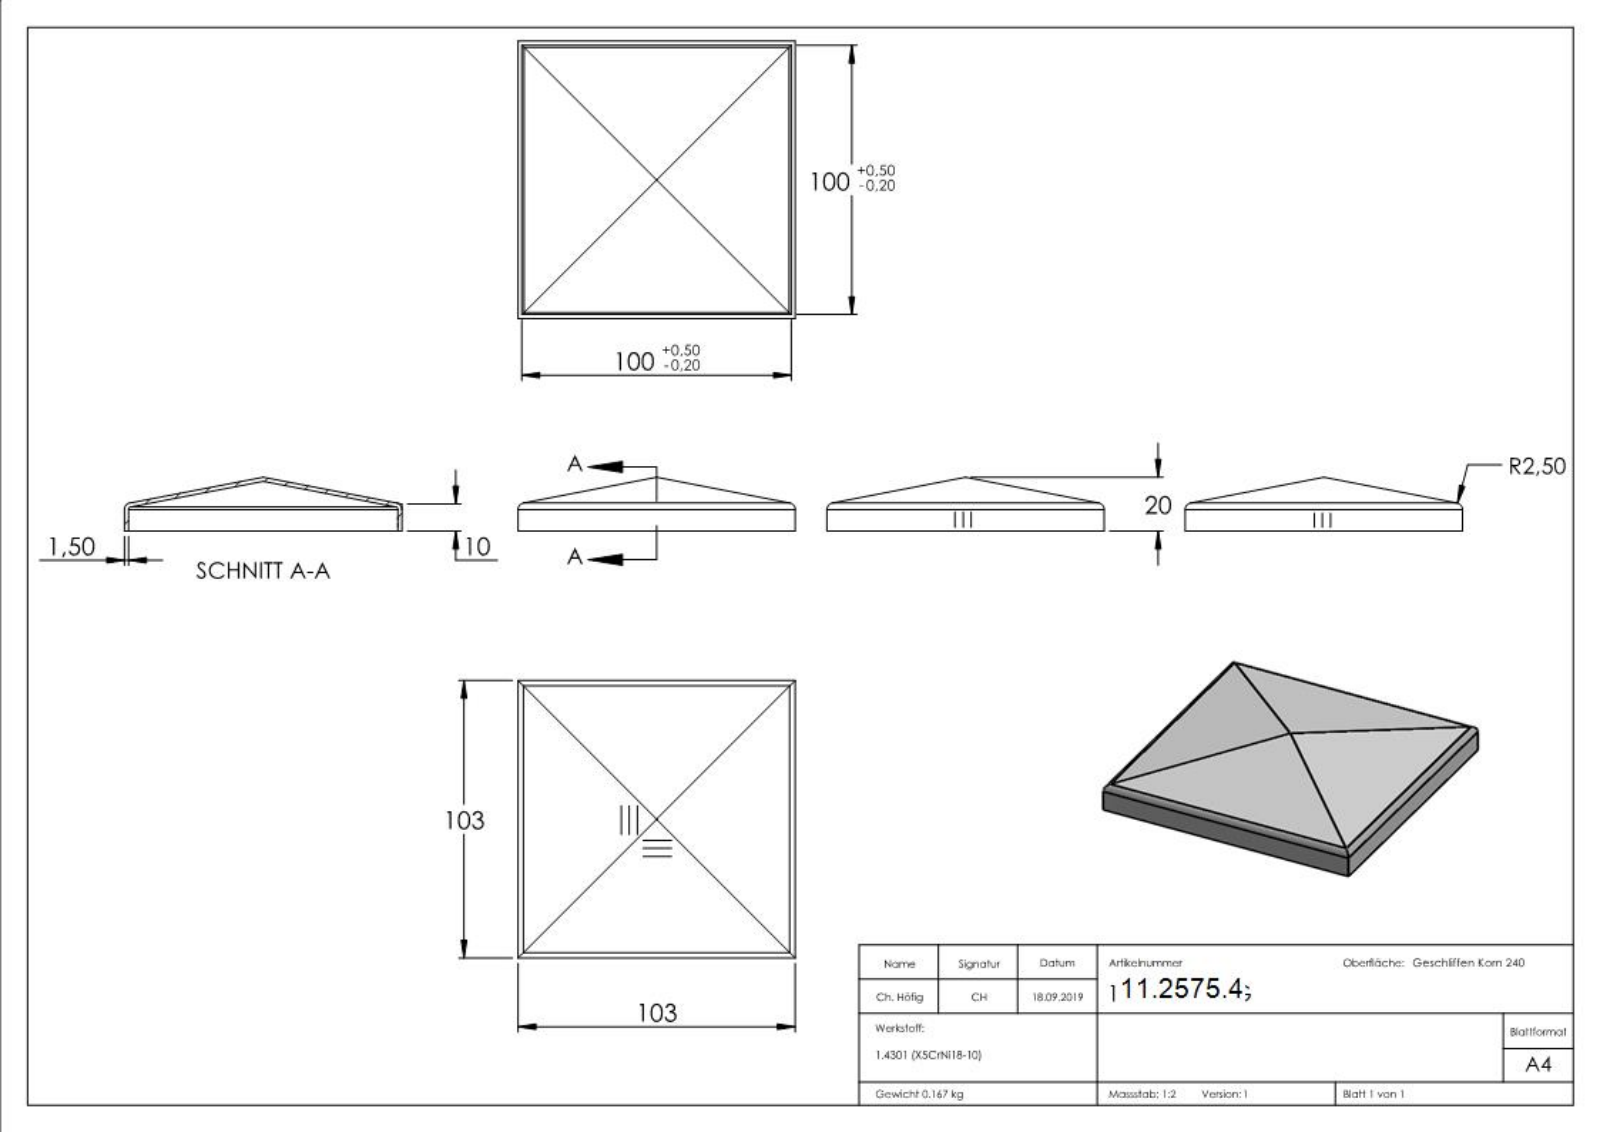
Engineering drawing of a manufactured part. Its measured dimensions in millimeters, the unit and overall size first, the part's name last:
Units: millimetres
Overall size (bounding box): 103 × 103 × 20
Partial cylindrical surfaces — rounded edges, fillets, slot ends (radius × count): R1 ×4, R2.5 ×4, R0.1 ×2
Main face-to-face distances: 1.5, 101.5, 103, 100, 1.4, 100.1, 101.6, 0.75, 2.2, 1.96
Volume: 21 167 mm³ · Surface area: 28 845 mm²
Bodies: 1 solid, 260 faces (150 planar, 12 cylindrical, 98 other)
Part name (STEP PRODUCT): 165-100V2AG
STEP written by: SolidWorks 2015 (CONFIG_CONTROL_DESIGN)
